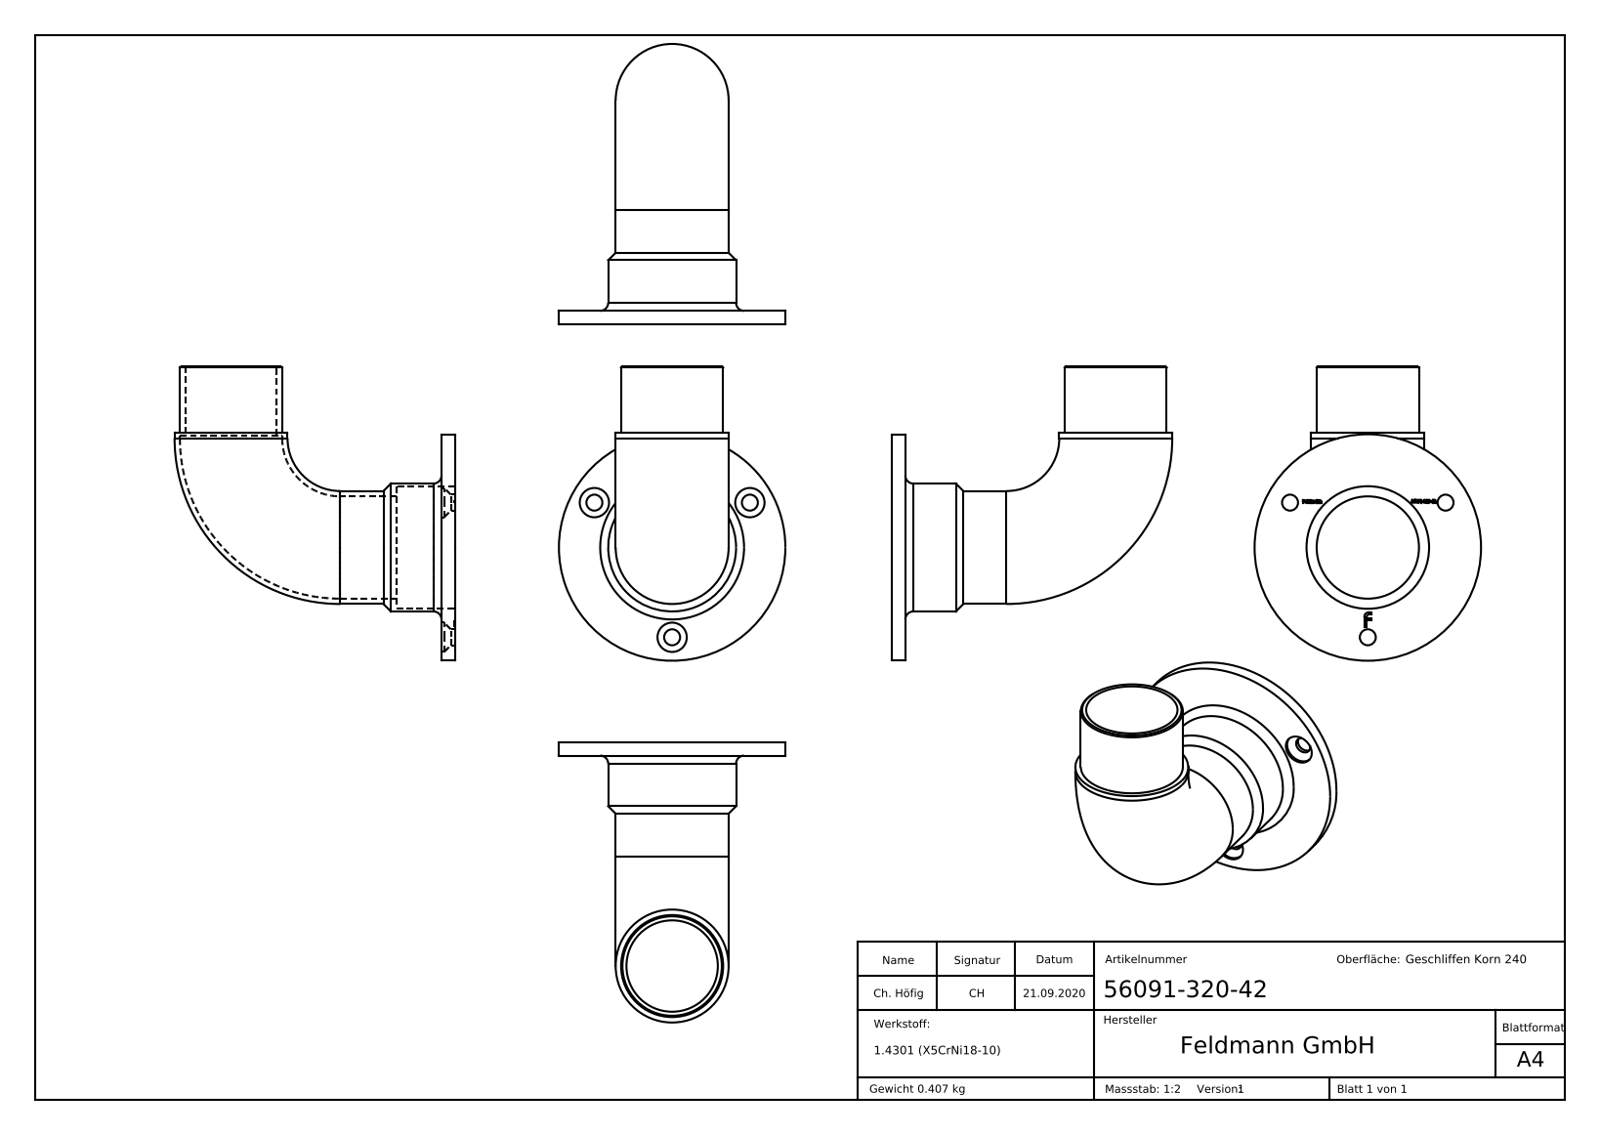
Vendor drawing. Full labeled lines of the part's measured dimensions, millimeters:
Part name (STEP PRODUCT): 56091-320-42
STEP written by: SolidWorks 2018 (CONFIG_CONTROL_DESIGN)
Units: millimetres
Bodies: 1 solid, 296 faces (153 planar, 15 cylindrical, 128 other)
Overall size (bounding box): 110.5 × 105.2 × 85
Volume: 51 469 mm³ · Surface area: 44 168 mm²
Round holes (diameter × count): ⌀6 ×3, ⌀11 ×3, ⌀38.4 ×2, ⌀34.3 ×1, ⌀46 ×1
Round bosses / shafts (diameter × count): ⌀42.4 ×2, ⌀85 ×1, ⌀48 ×1, ⌀38.3 ×1
Main face-to-face distances: 5, 22, 17, 1, 26, 25, 4.9, 21.9, 0.91, 25.15
Hole centre spacings: 33.7, 58.37, 58.38
